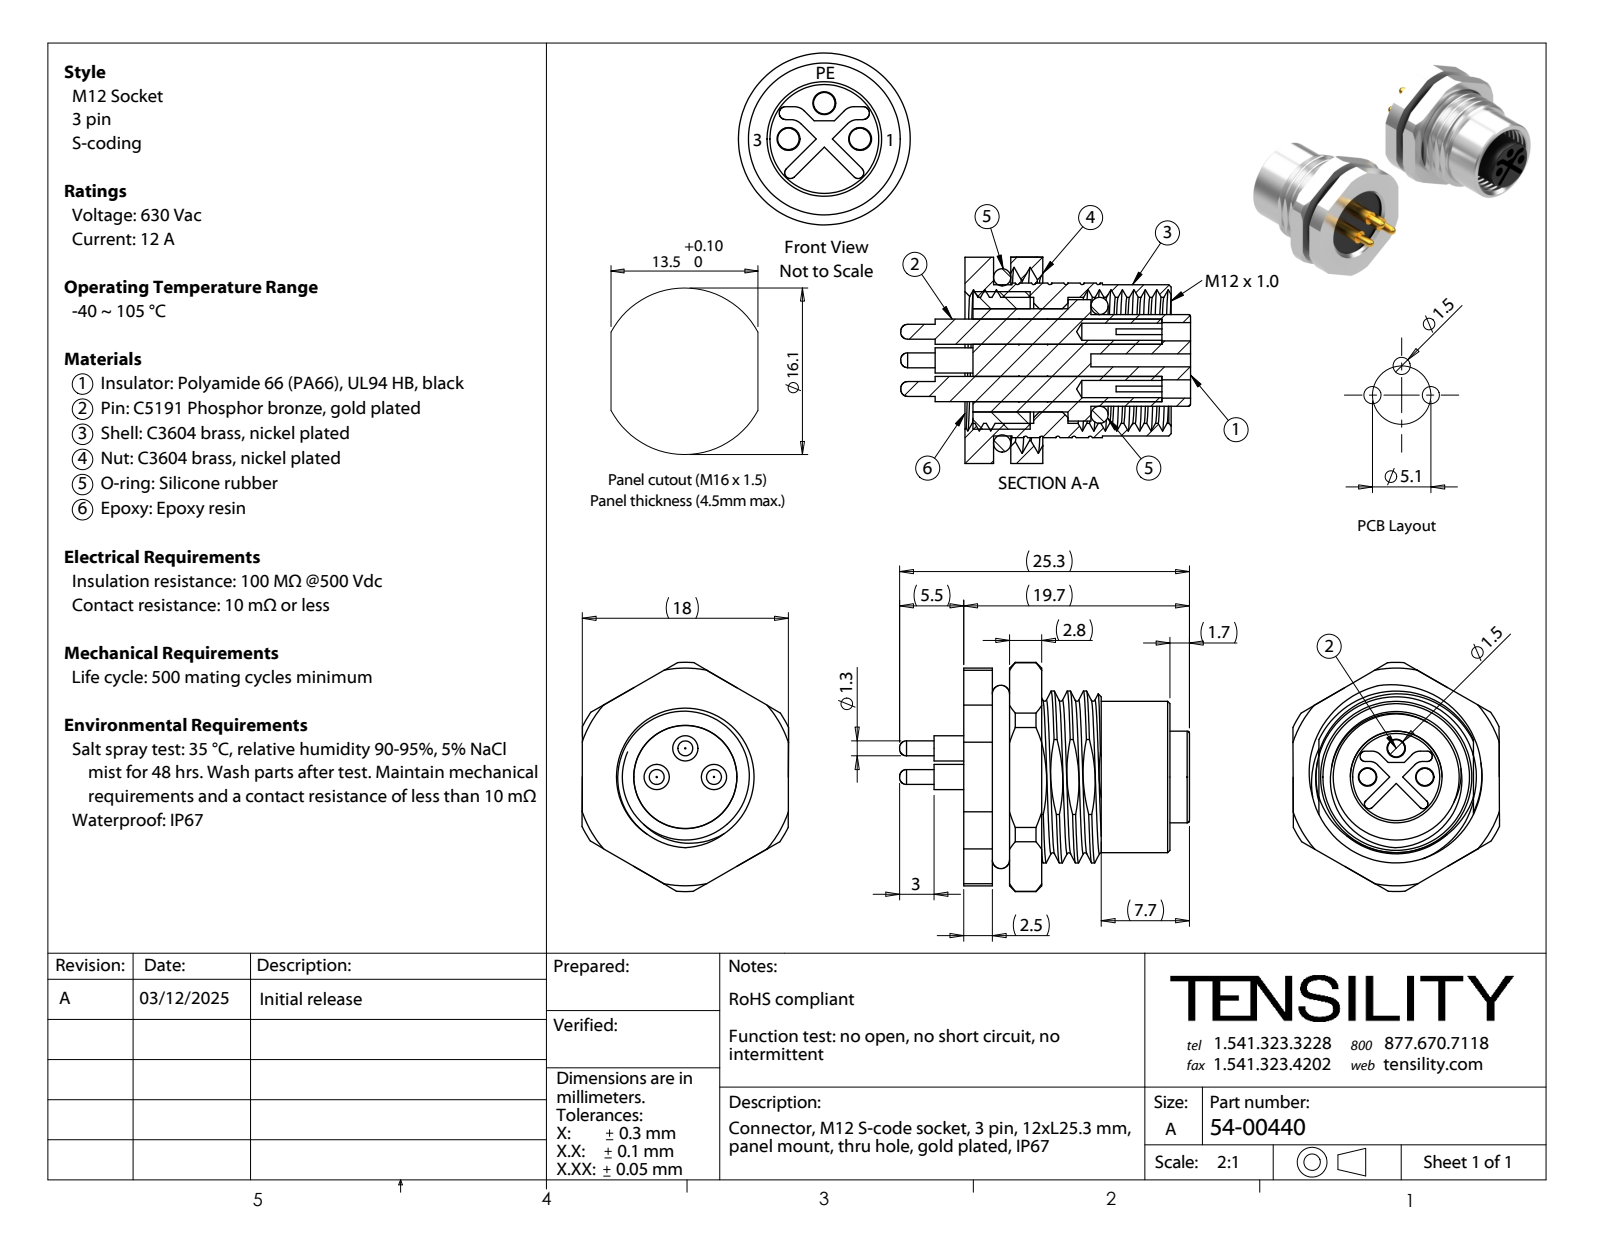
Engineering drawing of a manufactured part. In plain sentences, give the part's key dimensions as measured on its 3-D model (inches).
The part is named "54-00440-02; 54-00440-06; 54-00440-03; 54-00440-04 (+3 more)". Its 3-D file was written by "SolidWorks 2021 (CONFIG_CONTROL_DESIGN)". It is 9 solids with 293 faces: 95 planar, 119 cylindrical and 79 other. Overall it measures 0.996 by 0.787 by 0.71 inches. Its volume is 0.177 cubic inches and its surface area 8.692 square inches. Round holes: 3 of diameter 0.059, 3 of diameter 0.063, 1 of diameter 0.354, 1 of diameter 0.433, 1 of diameter 0.551. Round bosses or shafts: 3 of diameter 0.087, 3 of diameter 0.051, 1 of diameter 0.52, 1 of diameter 0.472, 1 of diameter 0.417, 1 of diameter 0.315. Partial cylindrical surfaces (rounded edges, fillets, slot ends): 4 of radius 0.039, 2 of radius 0.016, 2 of radius 0.018, 1 of radius 0.295, 1 of radius 0.374, 1 of radius 0.394. The main face-to-face distances are 0.098, 0.709, 0.13, 0.197, 0.028, 0.071, 0.031, 0.157, 0.169, 0.059. The hole center spacings are 0.098, 0.139, 0.197.
